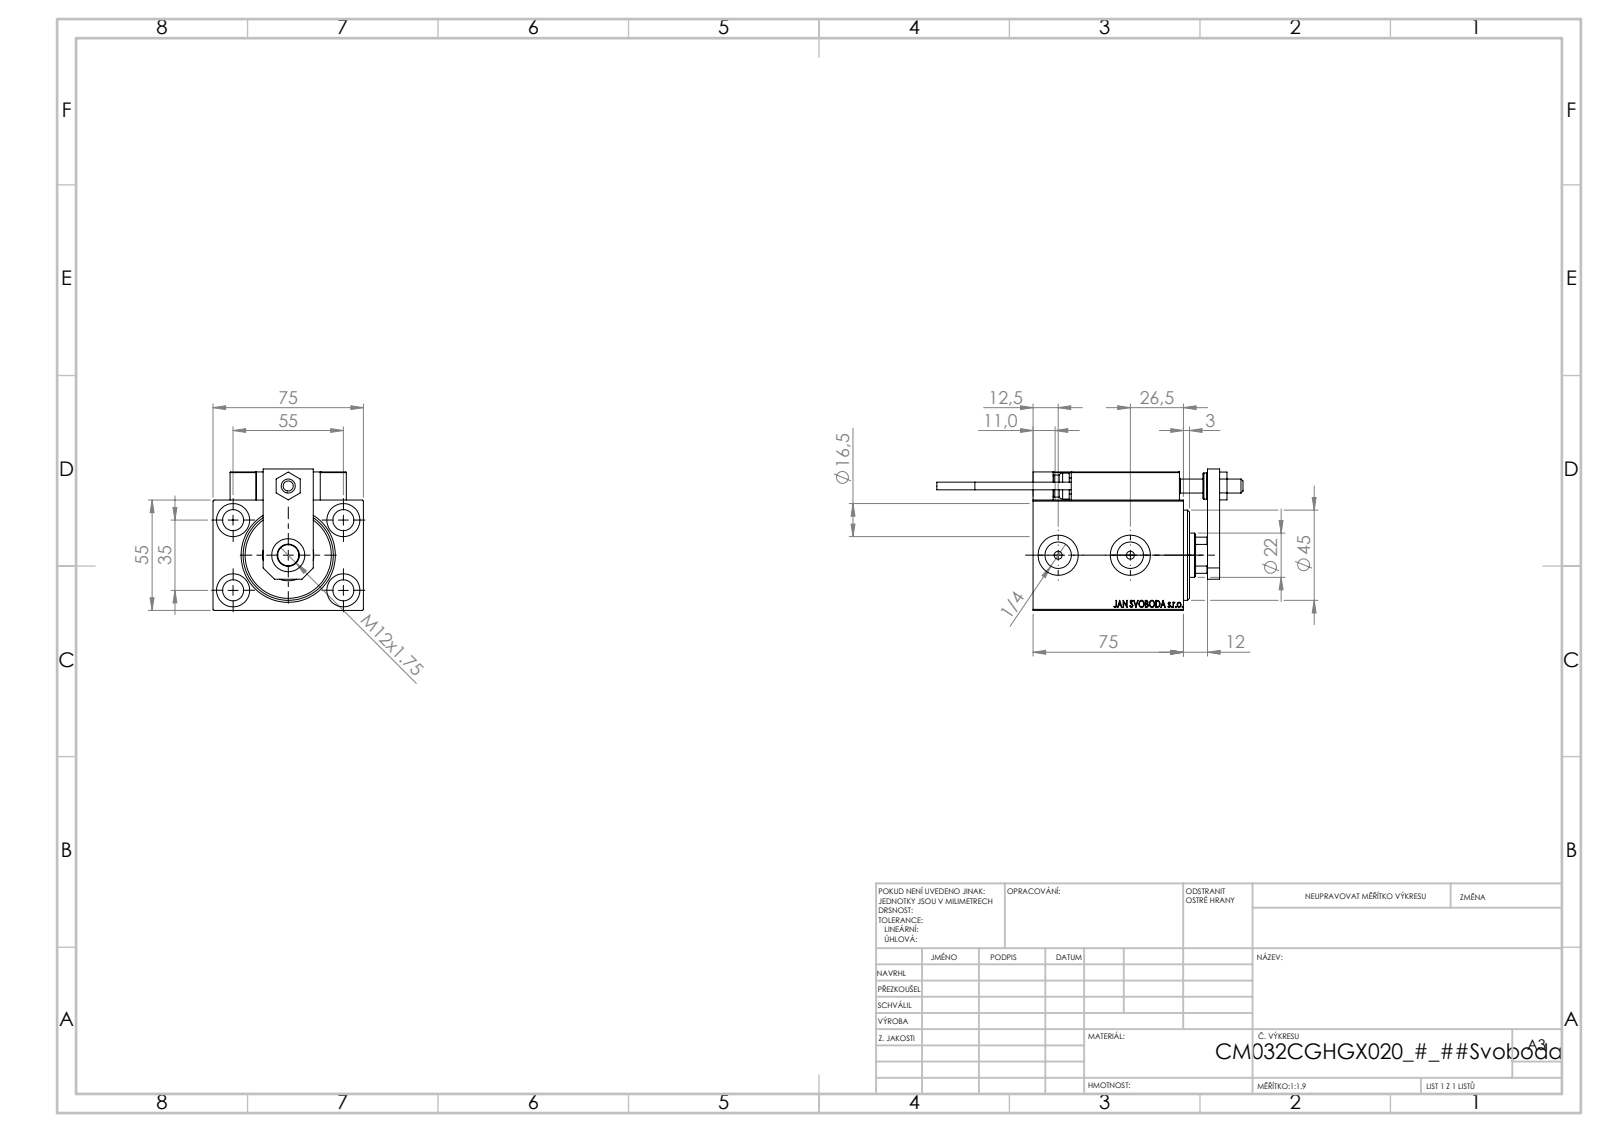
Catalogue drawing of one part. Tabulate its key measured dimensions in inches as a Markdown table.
| quantity | value |
| --- | --- |
| part name | TYC_L79; V450CM_VC_B; ZARAZKA; V450CM_C_Body (+7 more) |
| STEP written by | SolidWorks 2019 (CONFIG_CONTROL_DESIGN) |
| units | inches |
| bodies | 23 solids, 1282 faces (560 planar, 188 cylindrical, 534 other) |
| overall size | 6.012 × 2.953 × 2.776 |
| volume | 19.11 in³ |
| surface area | 131 in² |
| round holes (diameter × count) | 0.157 × 6, 0.315 × 5, 0.413 × 5, 0.65 × 5, 0.126 × 4, 0.197 × 2, 0.518 × 2, 0.787 × 2, 0.276 × 1, 0.866 × 1, 1.004 × 1, 1.26 × 1 |
| round bosses / shafts (diameter × count) | 0.197 × 2, 0.15 × 2, 0.512 × 1, 0.433 × 1 |
| partial cylindrical surfaces (radius × count) | 0.012 × 30, 0.118 × 2, 0.413 × 1 |
| main face-to-face distances | 2.165, 2.953, 0.551, 0.394, 0.472, 0.276, 2.717, 0.984, 0.787, 0.591 |
| hole center spacings | 1.283, 0.448, 0.787, 1.066, 1.165, 1.169, 1.273, 1.371 |
